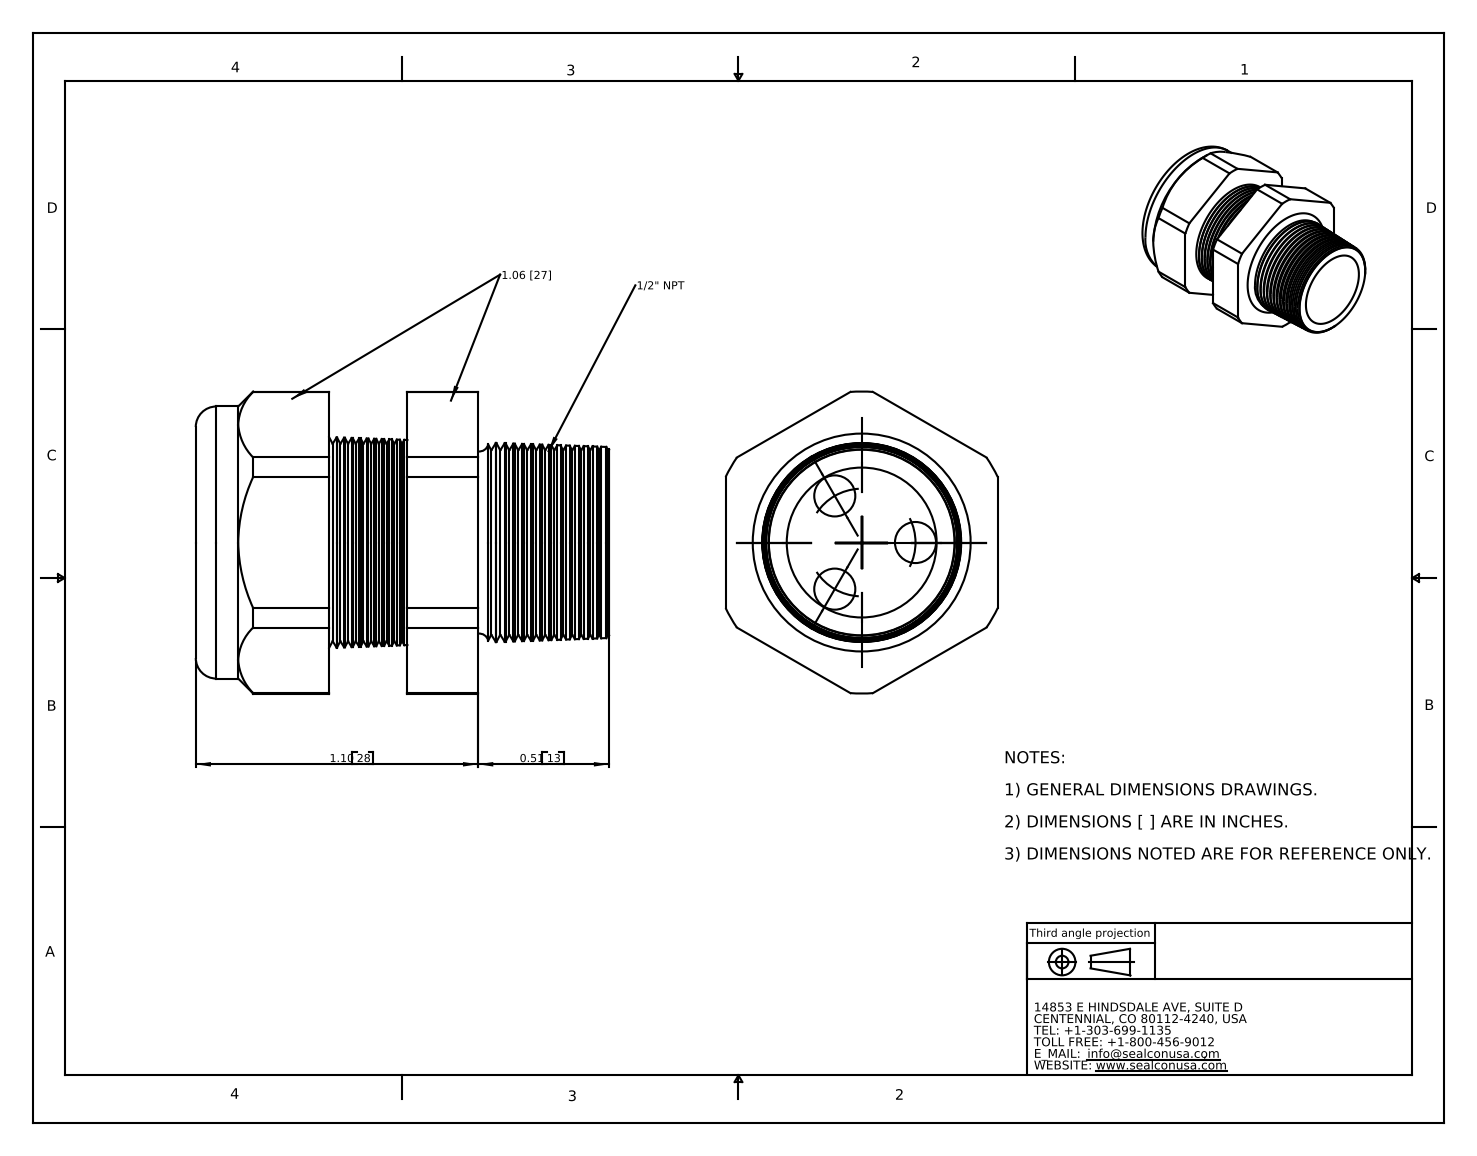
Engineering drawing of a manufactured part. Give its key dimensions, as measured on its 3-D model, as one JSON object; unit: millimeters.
{"part_name": "CD16N2-BK", "step_written_by": "SolidWorks 2007 (CONFIG_CONTROL_DESIGN)", "units": "millimeters", "bodies": {"solids": 2, "faces": 204, "planar": 20, "cylindrical": 26, "other": 158}, "overall_size": [40.9, 29.9, 26.9], "volume_mm3": 12200, "surface_area_mm2": 8381, "round_holes": [[4.1, 3], [14.7, 1], [15.2, 1]], "round_bosses_or_shafts": [[26.9, 1]], "partial_cylinders_radius": [[14.9, 1]], "face_to_face_distances": [26.9, 7.7, 14.7, 7, 13.2, 20.9, 27.9, 8.9, 4.3, 12], "hole_center_spacings": [9.2, 5.3, 5.3]}
